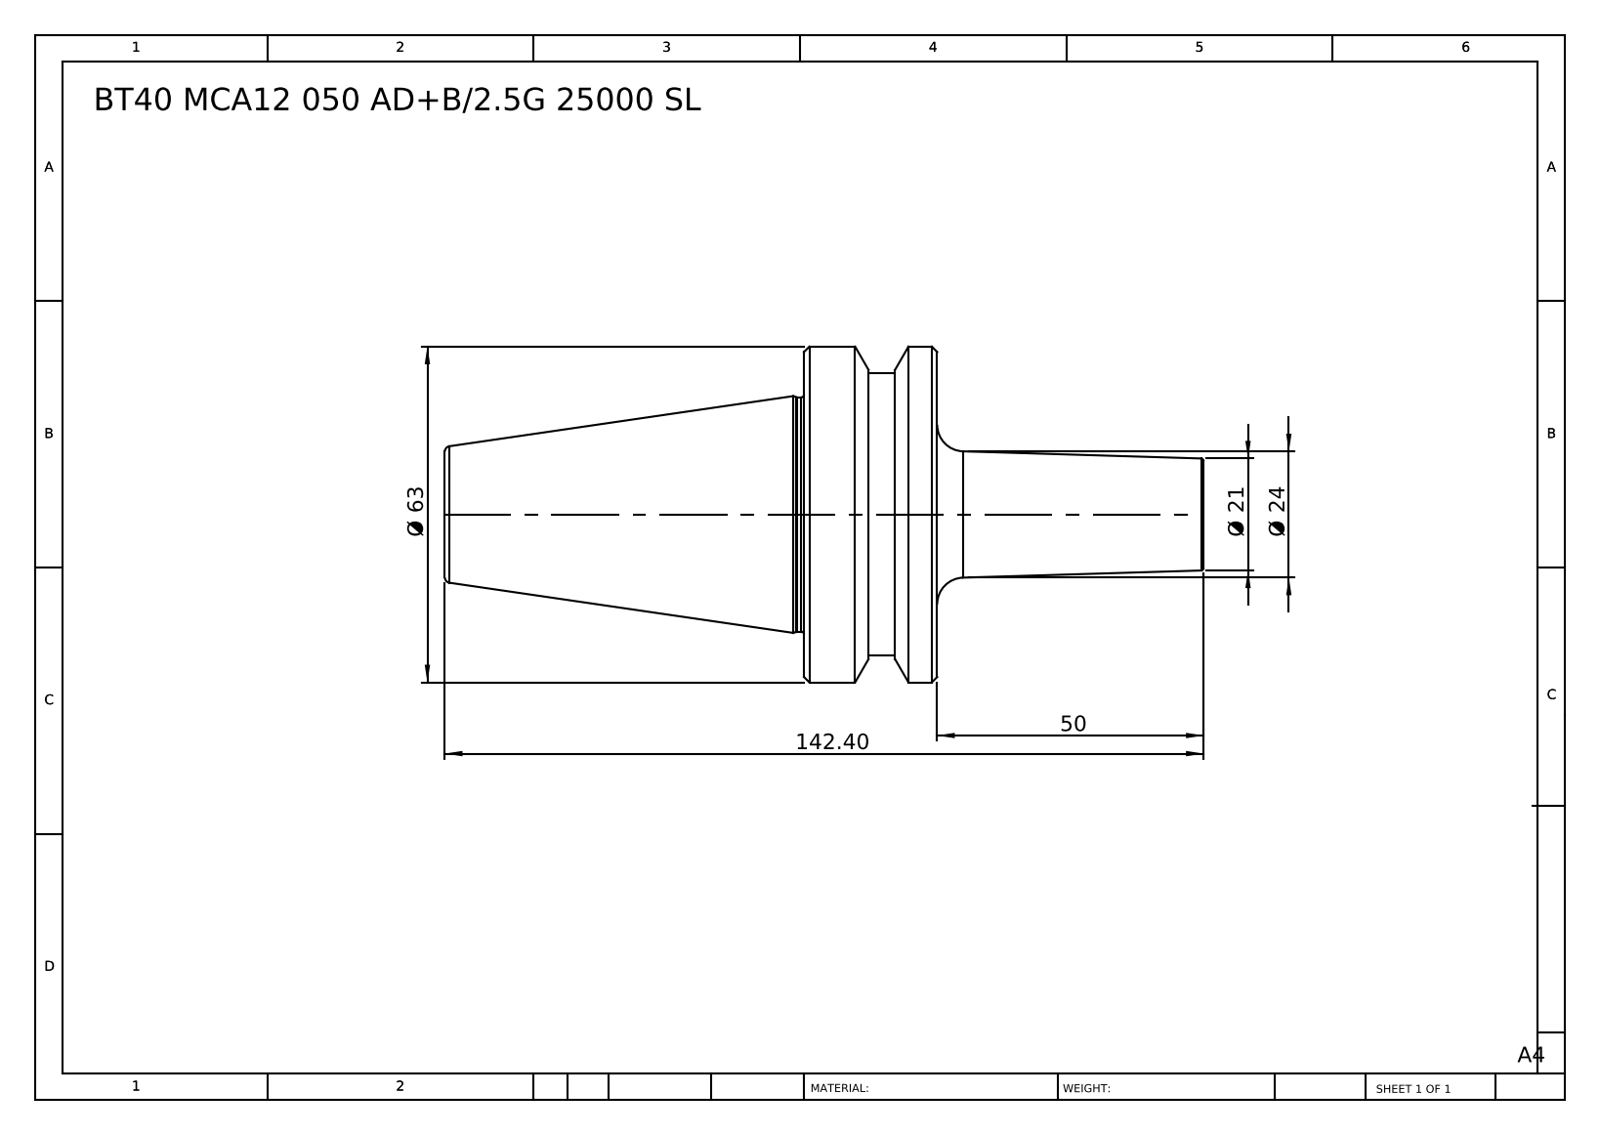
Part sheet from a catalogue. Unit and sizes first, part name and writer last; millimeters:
Units: millimetres
Overall size (bounding box): 142.4 × 63 × 63
Round bosses / shafts (diameter × count): ⌀63 ×1, ⌀53 ×1, ⌀44 ×1
Main face-to-face distances: 25, 92.4, 67.4, 50, 75, 142.4, 62.9, 12.9, 12.1, 79.5
Volume: 158 663 mm³ · Surface area: 21 609 mm²
Bodies: 1 solid, 38 faces (6 planar, 8 cylindrical, 24 other)
Part name (STEP PRODUCT): BT40 MCA12 050 AD+B-2.5G 25000 SL
STEP written by: SolidWorks 2014 (CONFIG_CONTROL_DESIGN)
